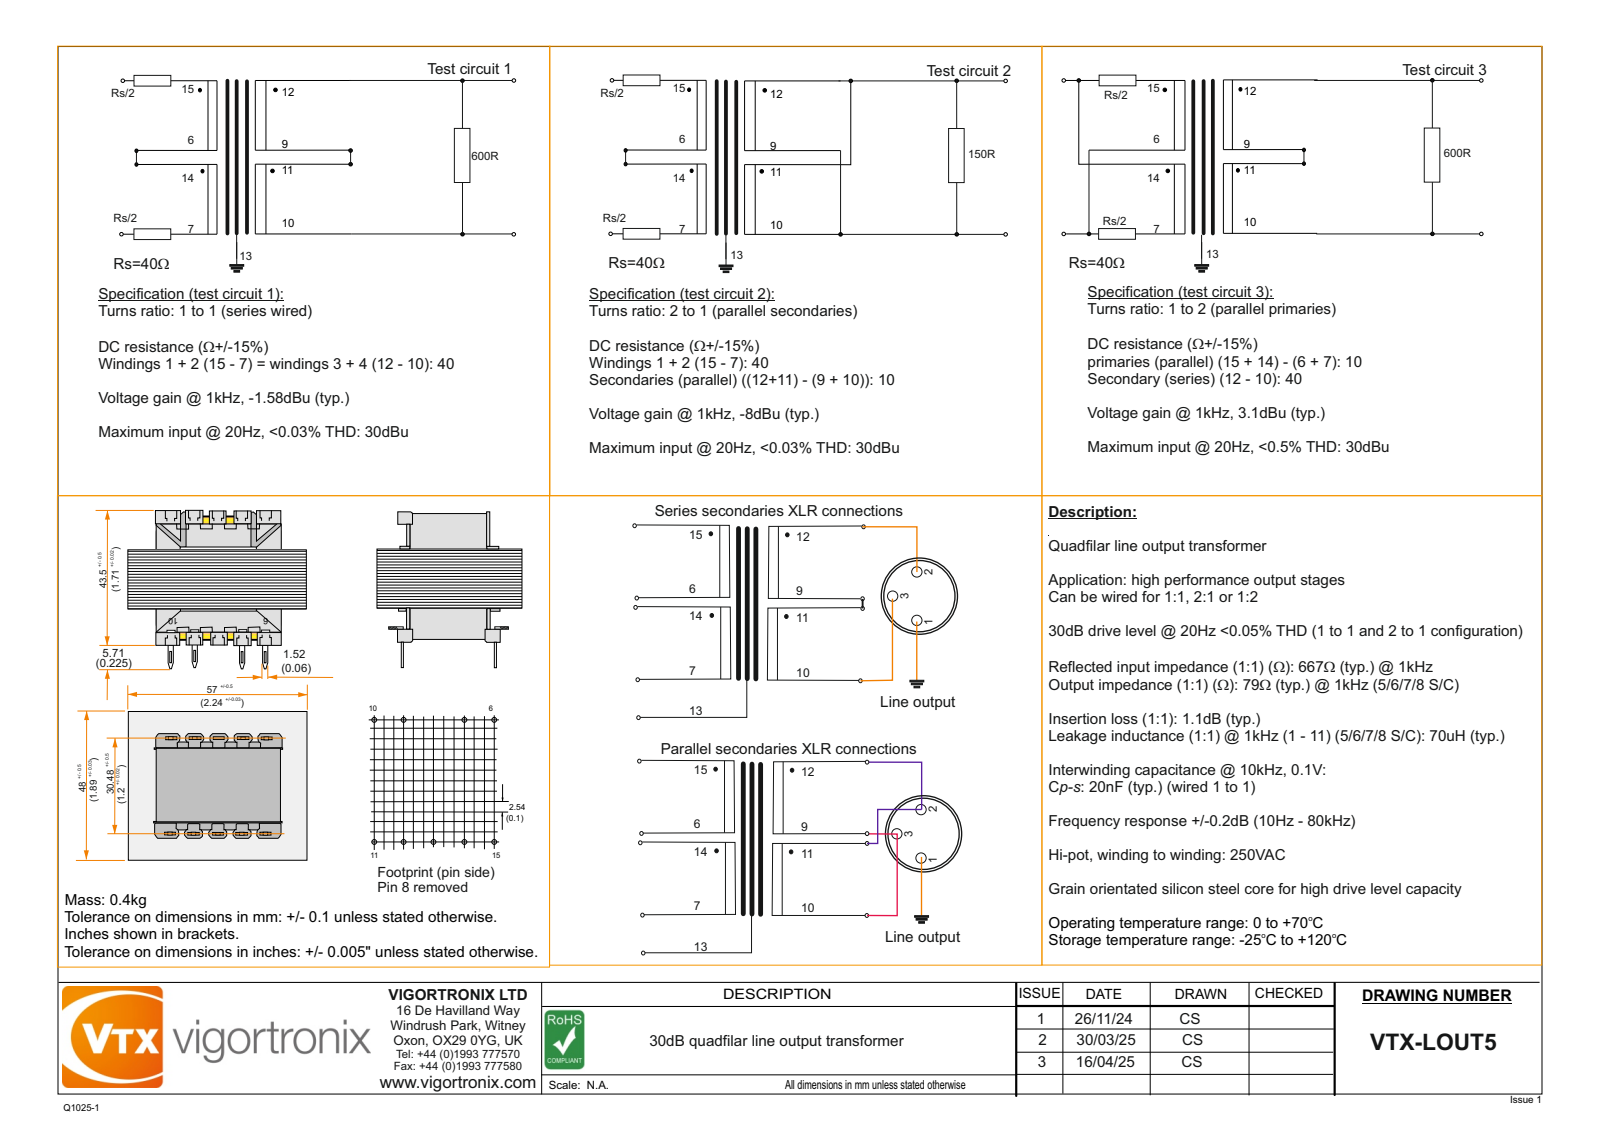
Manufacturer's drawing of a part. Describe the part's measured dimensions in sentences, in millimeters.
The part is named "35 x 3-4 inch S0200 Bobbin; Terminal Pin 903 Bent; VTX-LOUT5; E UK35 (+2 more)". Its 3-D file was written by "SolidWorks 2024 (AUTOMOTIVE_DESIGN)". It is 107 solids with 1733 faces: 1473 planar, 213 cylindrical and 47 other. Overall it measures 57 by 49.14 by 47.5 millimeters. Its volume is 65 906 cubic millimeters and its surface area 234 900 square millimeters. Partial cylindrical surfaces (rounded edges, fillets, slot ends): 48 of radius 0.1, 36 of radius 0.63, 20 of radius 0.2, 20 of radius 1.5, 8 of radius 1, 5 of radius 0.25, 4 of radius 7, 2 of radius 0.5. The main face-to-face distances are 0.4, 0.8, 1.2, 1.6, 2, 2.4, 2.8, 3.2, 3.6, 4.
